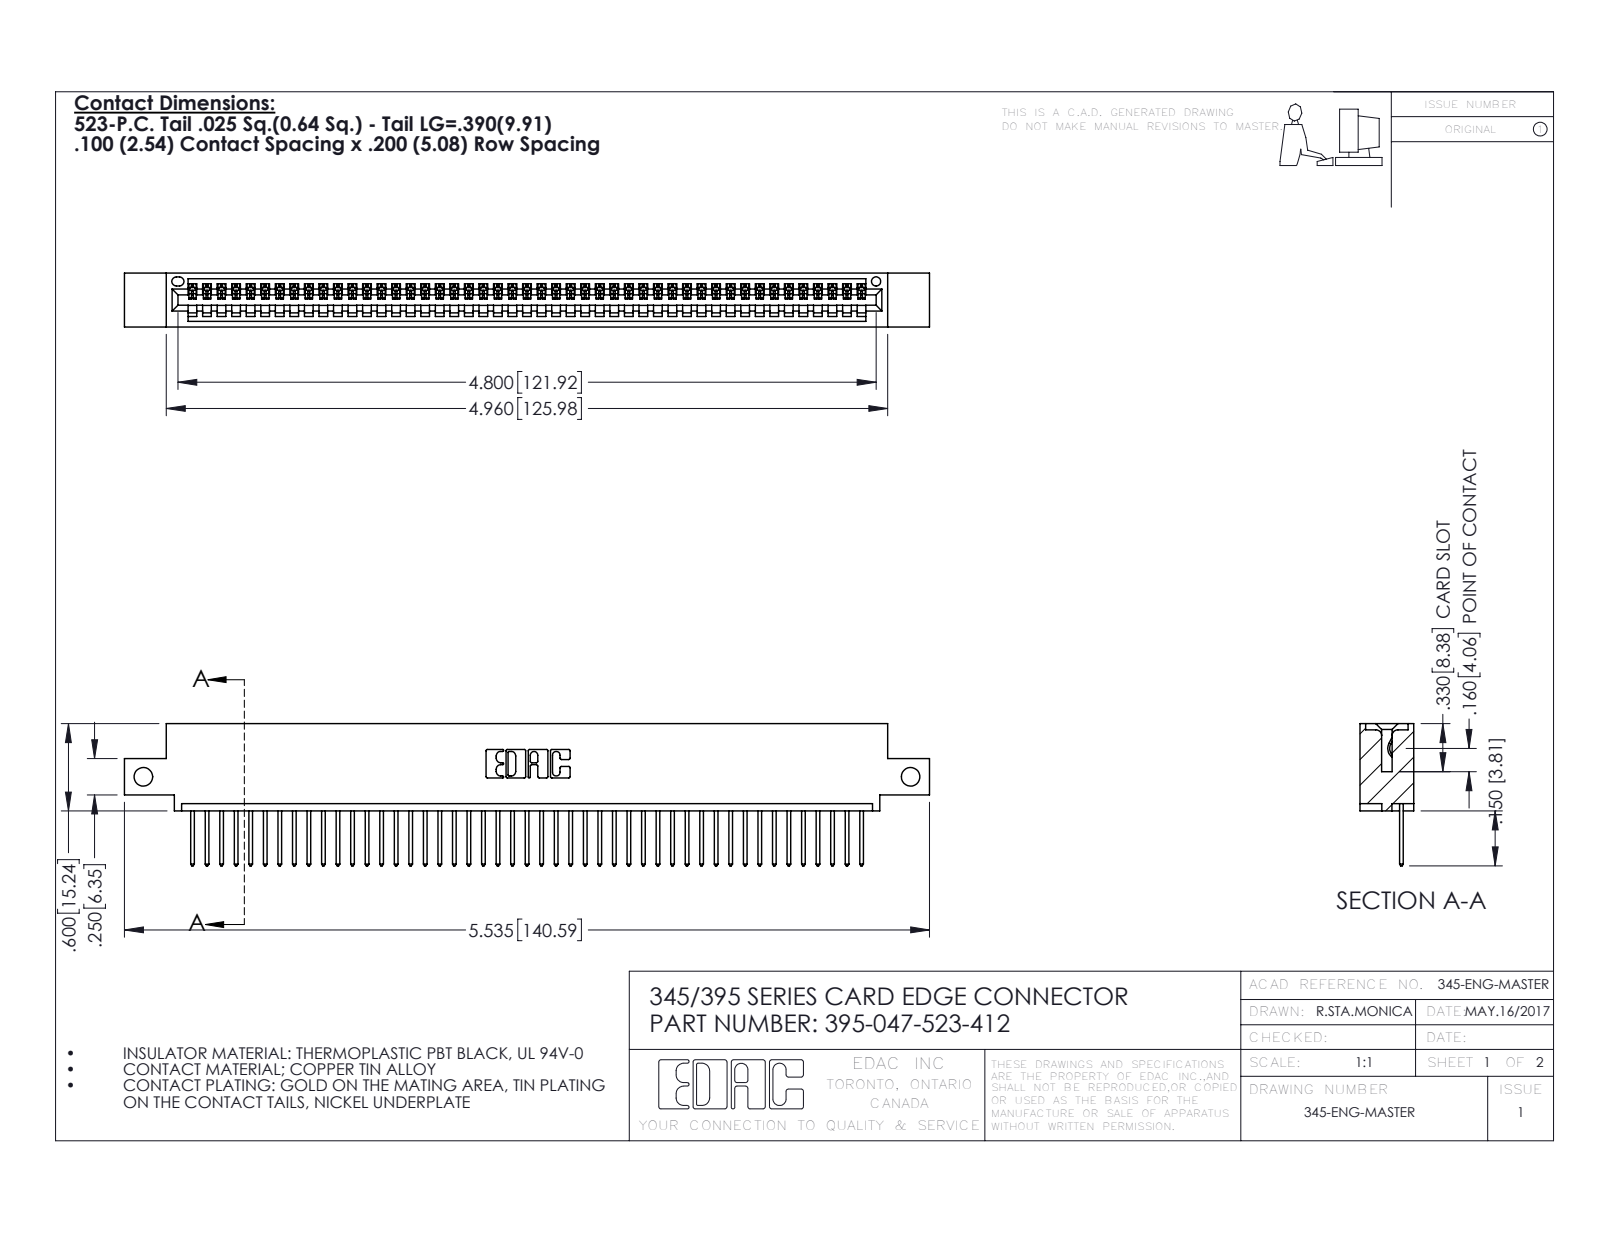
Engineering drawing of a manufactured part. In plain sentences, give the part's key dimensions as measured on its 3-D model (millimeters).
The part is named "345 Part_0.110 Offset - Side Mount; 345-292-001_345-293-123; 395-047-523-412". Its 3-D file was written by "SolidWorks 2016 (CONFIG_CONTROL_DESIGN)". It is 48 solids with 2856 faces: 1964 planar, 892 cylindrical and 0 other. Overall it measures 140.6 by 24.8 by 9.4 millimeters. Its volume is 13 200 cubic millimeters and its surface area 17 620 square millimeters. Round holes: 2 of diameter 3.3, 1 of diameter 1.6. Partial cylindrical surfaces (rounded edges, fillets, slot ends): 94 of radius 0.2, 94 of radius 0.3, 22 of radius 0.3, 6 of radius 0.2, 6 of radius 0.8, 3 of radius 0.7, 2 of radius 0.8, 2 of radius 1. The main face-to-face distances are 1.8, 7.6, 9.4, 5.1, 2.5, 6.9, 0.6, 5.7, 3.8, 1.8. The hole center spacings are 134.
